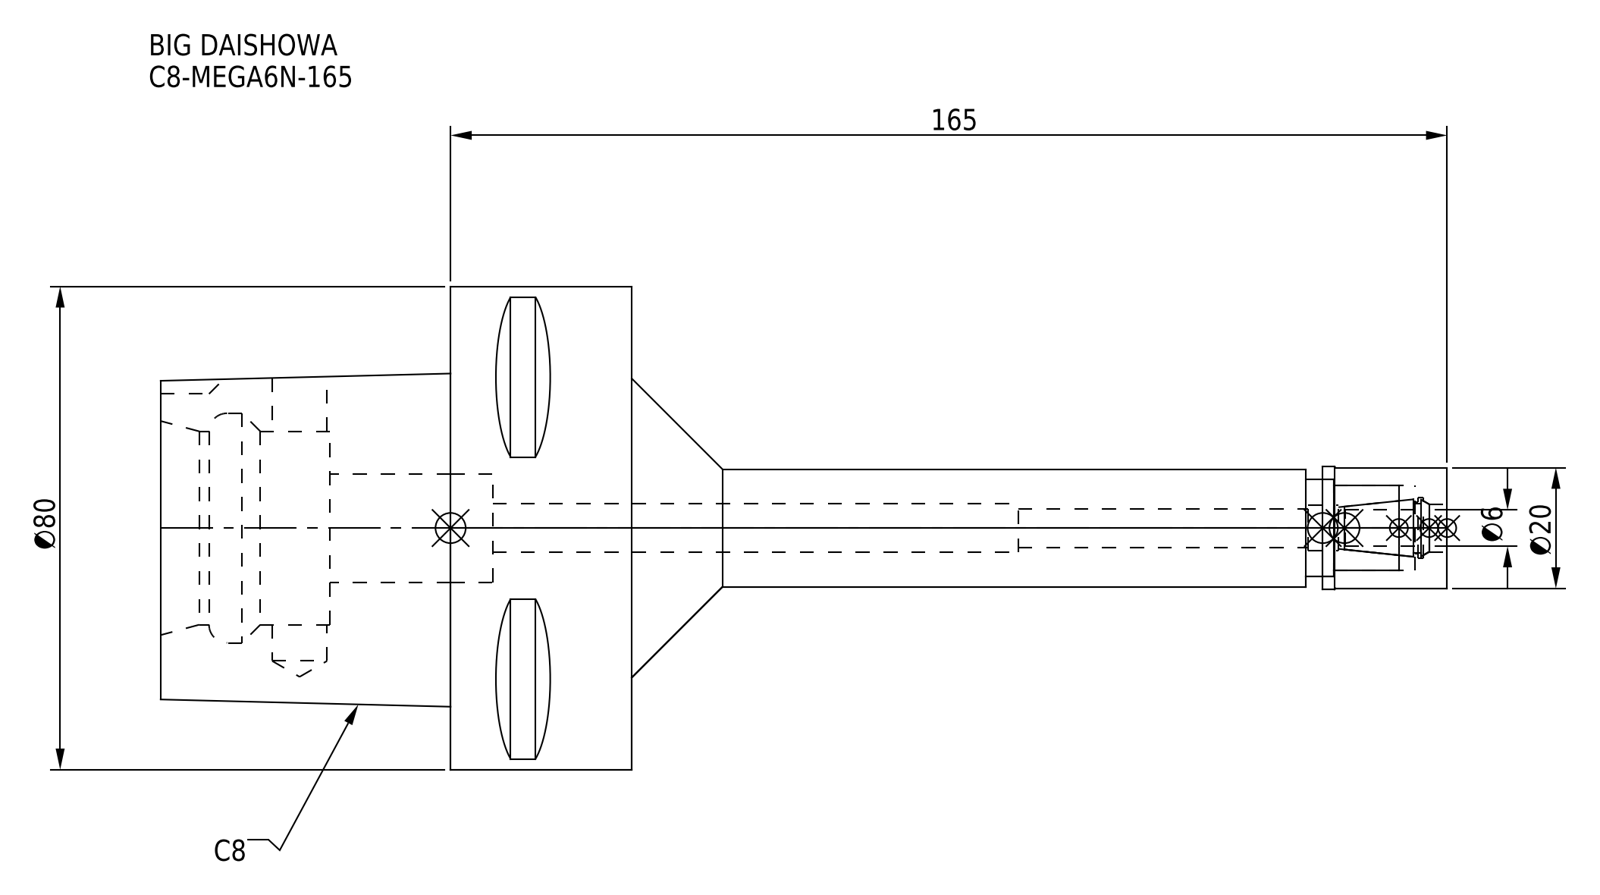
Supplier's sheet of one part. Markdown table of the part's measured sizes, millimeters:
| quantity | value |
| --- | --- |
| part name | C8-MEGA6N-165_1.stp; DXF_TEMP_ASSY_ASM_4_ASM.stp; MGN6_1.stp; C8-MEGA6N-165-060_ASM.stp (+3 more) |
| STEP written by | SolidWorks 2019 (CONFIG_CONTROL_DESIGN) |
| units | millimeters |
| bodies | 2 solids, 98 faces (39 planar, 41 cylindrical, 18 other) |
| overall size | 213 × 80 × 80 |
| volume | 266 629 mm³ |
| surface area | 44 469 mm² |
| round holes (diameter × count) | 6.4 × 1, 7.5 × 1, 7.9 × 1, 8 × 1, 8.5 × 1, 9.1 × 1, 10 × 1, 14 × 1, 16 × 1, 18 × 1, 32 × 1, 38 × 1 |
| round bosses / shafts (diameter × count) | 80 × 1, 20.3 × 1, 20 × 1, 19.5 × 1 |
| partial cylindrical surfaces (radius × count) | 6 × 1 |
| main face-to-face distances | 30, 48, 78, 20, 50, 28, 32.55, 70.68, 135, 165 |
